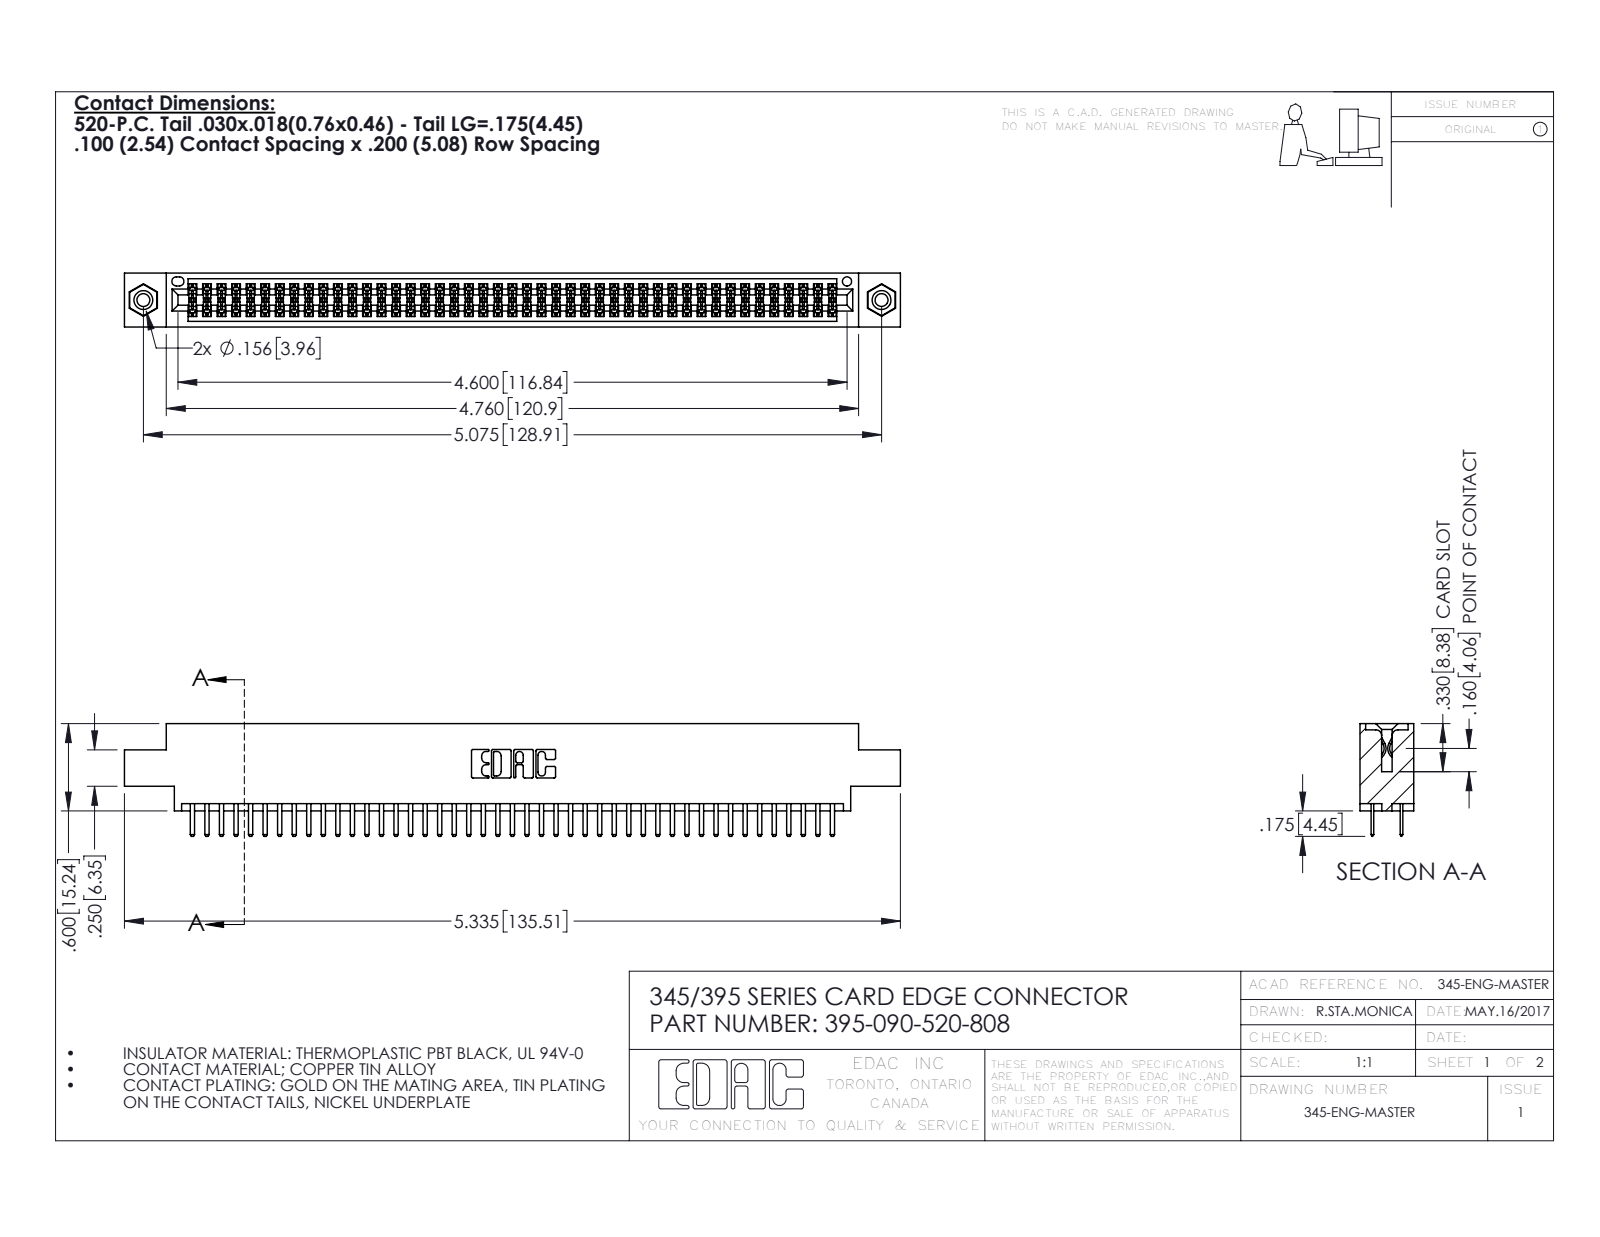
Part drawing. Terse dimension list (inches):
name: 345-250-001_345-250-003-102; 345 Part_0.170 Offset - 0.156 Dia-TI; 345-292-001_345-293-120; 395-090-520-808
written by: SolidWorks 2016 (CONFIG_CONTROL_DESIGN)
unit: in
bodies: 93 solids, 5050 faces (3266 planar, 1768 cylindrical, 16 other)
size: 5.335 × 0.775 × 0.37
volume: 0.795 in³; area: 30.06 in²
holes: 2× ⌀0.089, 2× ⌀0.125, 2× ⌀0.156, 1× ⌀0.064
bosses: 2× ⌀0.155
rounds: 135× R0.006, 94× R0.01, 22× R0.01, 6× R0.007, 6× R0.031, 3× R0.026, 2× R0.014, 2× R0.019
face distances: 0.072, 0.298, 0.2, 0.37, 0.098, 0.272, 0.025, 0.225, 0.022, 0.072
hole spacings: 0.27, 4.839, 5.075
